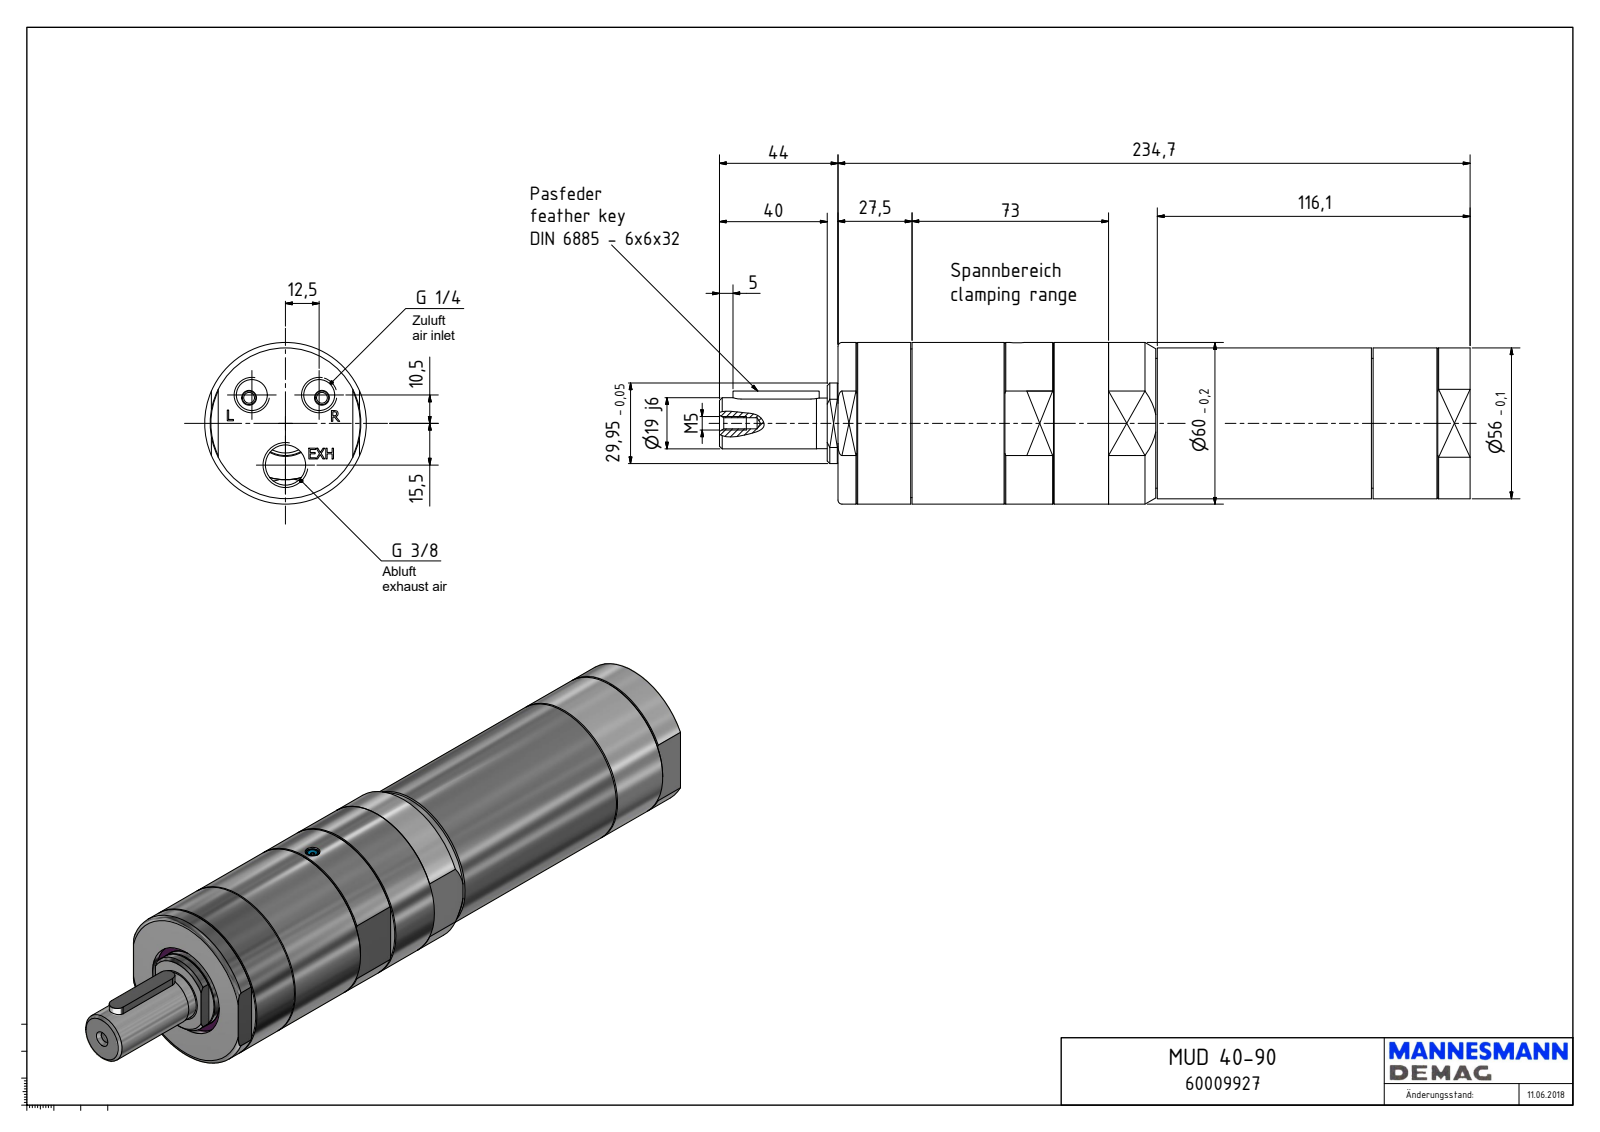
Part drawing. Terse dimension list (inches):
name: MUD 40-90_60009927
written by: Autodesk Inventor 2018 (AUTOMOTIVE_DESIGN)
unit: in
bodies: 1 solid, 213 faces (114 planar, 46 cylindrical, 53 other)
size: 10.972 × 2.362 × 2.362
volume: 38 in³; area: 93.96 in²
holes: 2× ⌀0.451, 1× ⌀0.061, 1× ⌀0.157, 1× ⌀0.163, 1× ⌀0.217, 1× ⌀0.589, 1× ⌀1.378, 1× ⌀1.437, 1× ⌀1.575, 1× ⌀1.905, 1× ⌀2.18
bosses: 1× ⌀2.362, 1× ⌀2.205, 1× ⌀2.172, 1× ⌀1.897, 1× ⌀1.179, 1× ⌀0.748, 1× ⌀0.74, 1× ⌀0.197
rounds: 2× R0.118, 2× R0.236, 1× R0.772, 1× R0.906, 1× R1.057
face distances: 9.24, 2.165, 0.024, 3.154, 4.571, 0.098, 2.067, 7.799, 1.441, 4.669
hole spacings: 0.643, 1.136, 0.61, 0.984
